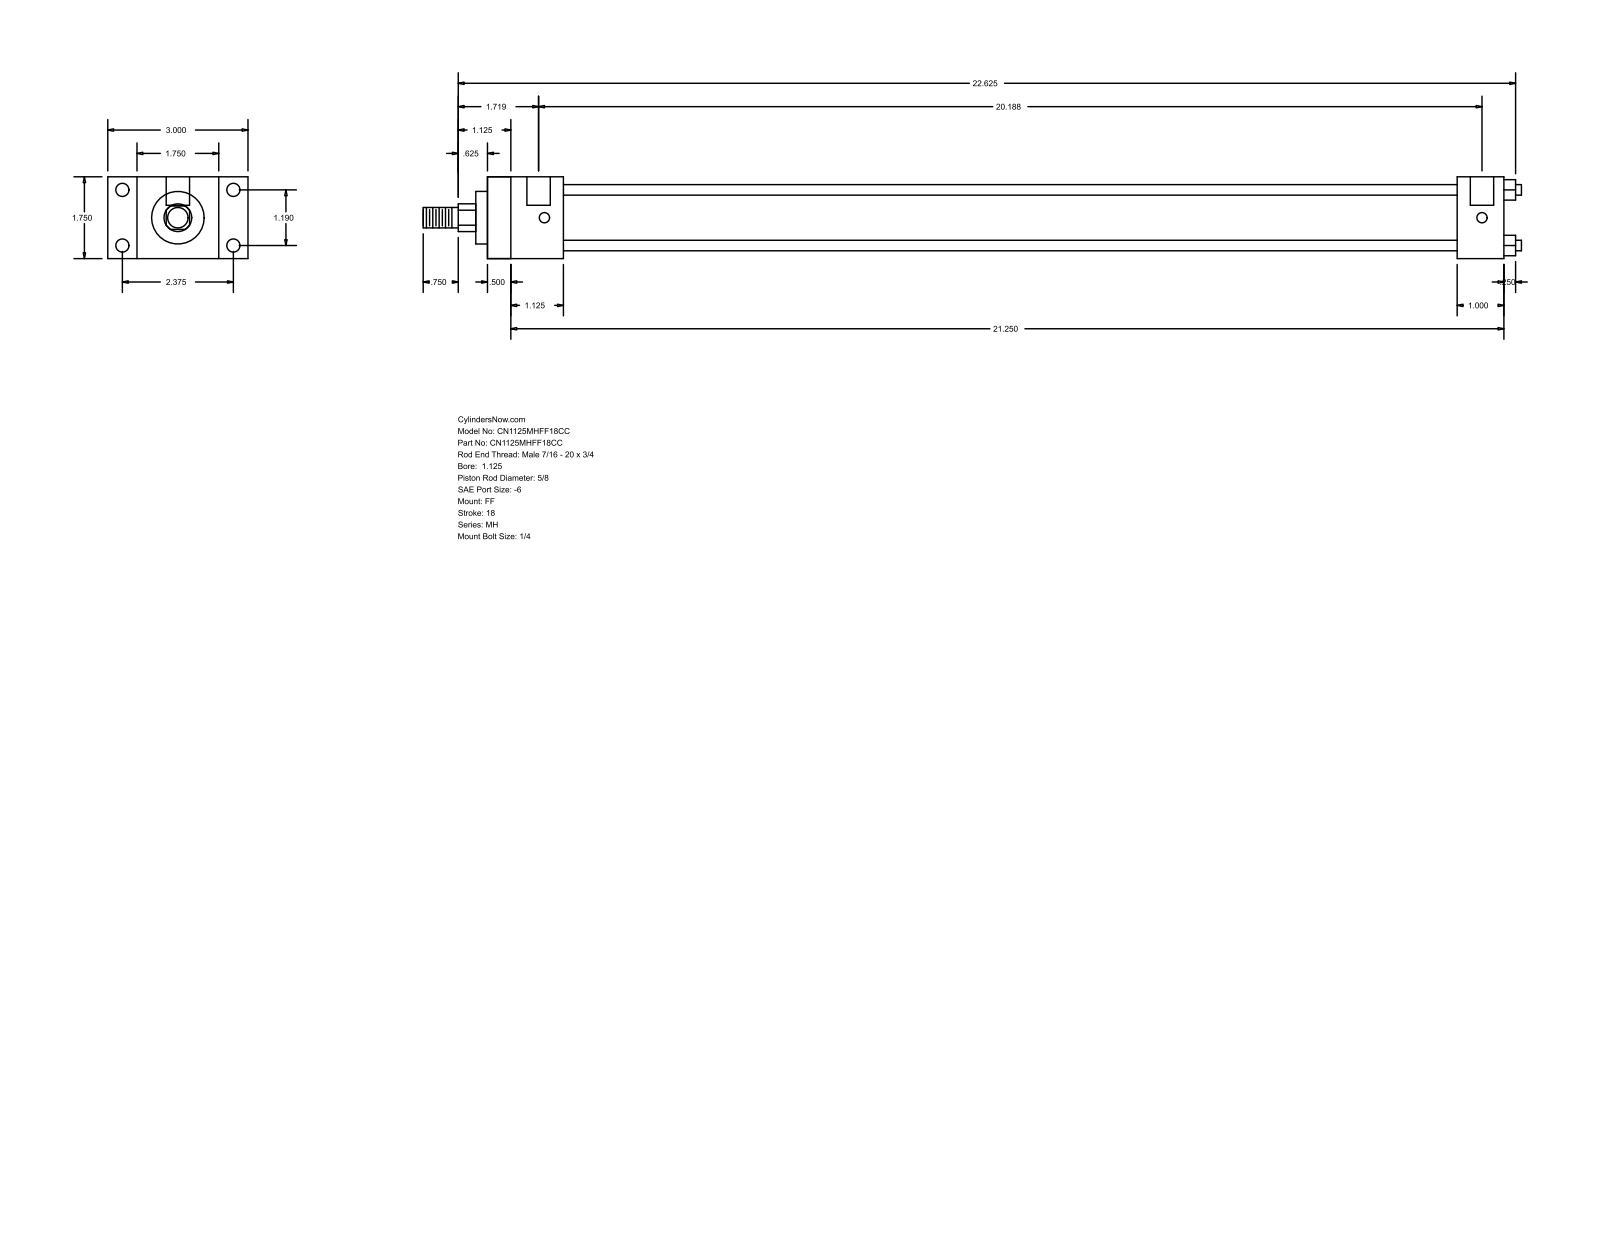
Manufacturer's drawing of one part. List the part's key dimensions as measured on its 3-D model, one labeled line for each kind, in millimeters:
Part name (STEP PRODUCT): MH_FF__0112_0.625
STEP written by: GSSL Pune (CONFIG_CONTROL_DESIGN)
Units: millimetres
Bodies: 0 solids, 92 faces (64 planar, 28 cylindrical, 0 other)
Overall size (bounding box): 596.9 × 76.2 × 44.45
Round holes (diameter × count): ⌀5.56 ×4, ⌀7.14 ×4, ⌀12.7 ×2
Round bosses / shafts (diameter × count): ⌀5.71 ×4, ⌀34.92 ×1, ⌀28.57 ×1, ⌀15.88 ×1, ⌀11.11 ×1
Partial cylindrical surfaces — rounded edges, fillets, slot ends (radius × count): R7.54 ×1
Main face-to-face distances: 44.46, 552.45, 12.69, 539.76, 15.87, 28.58, 60.33, 41.27, 527.04, 514.35
Hole centre spacings: 30.22, 60.32, 67.47, 509.59, 3.17, 512.76
